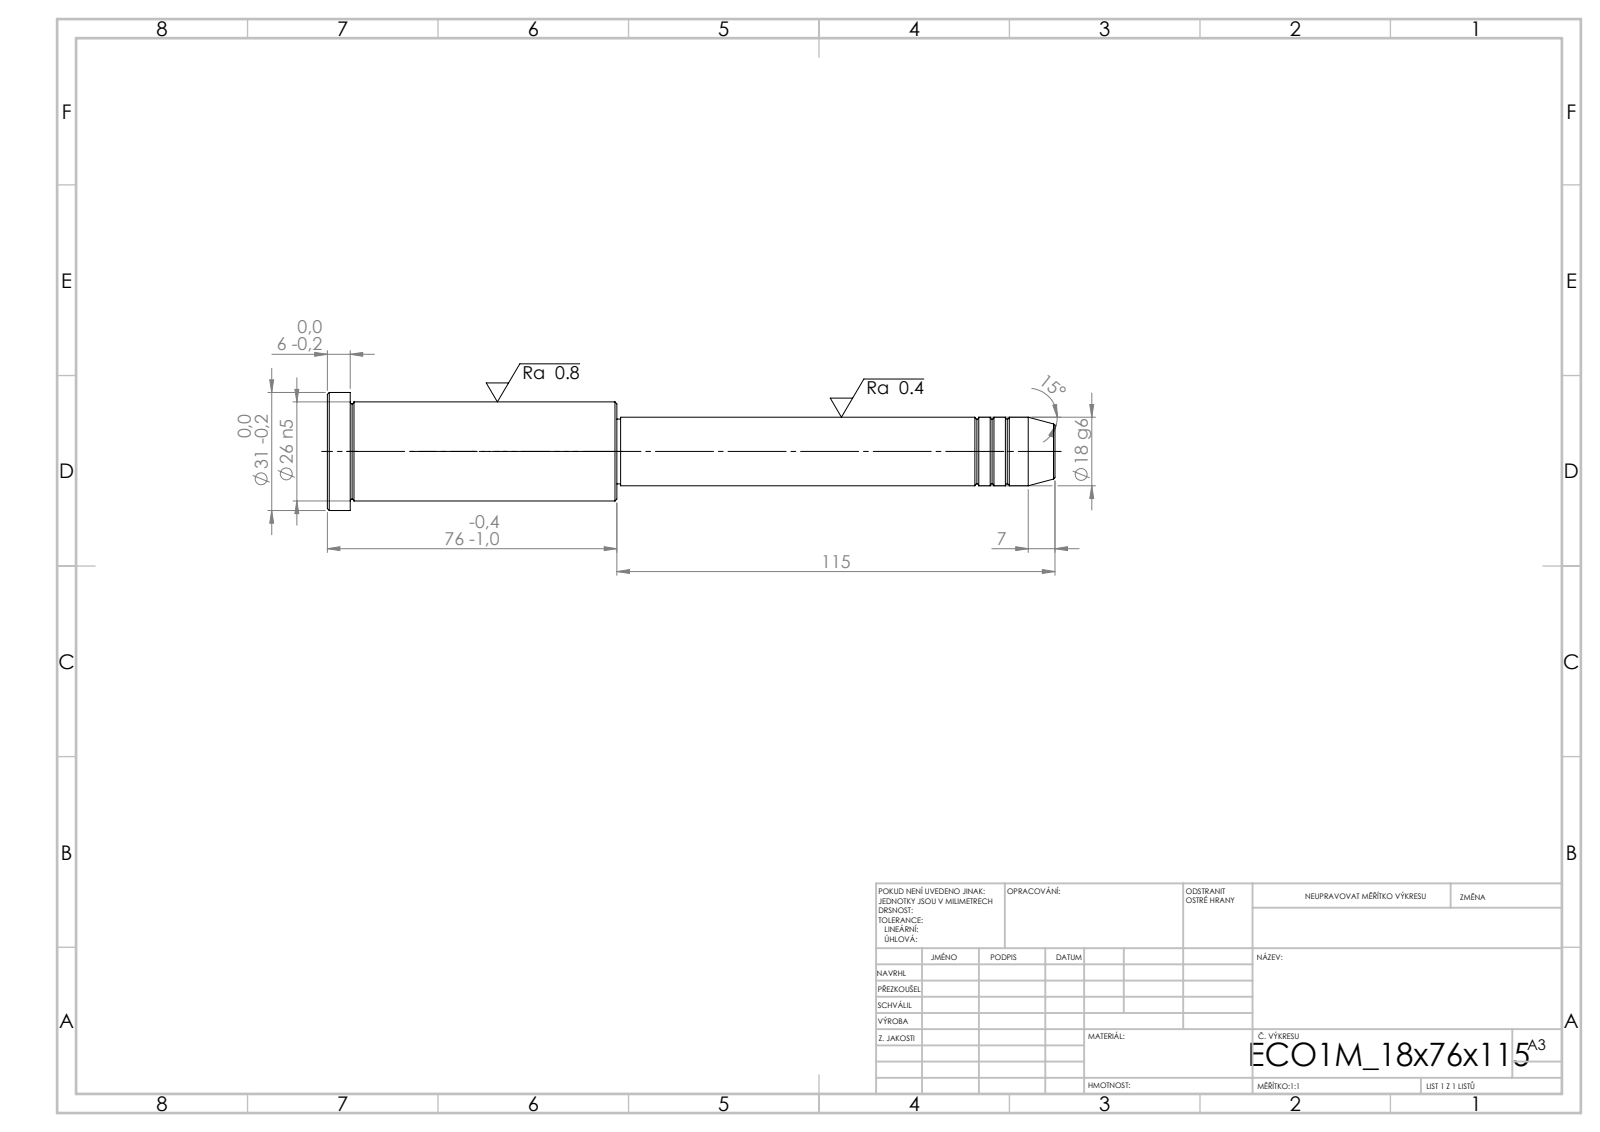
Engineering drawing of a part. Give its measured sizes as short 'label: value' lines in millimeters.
written by: SolidWorks 2019 (CONFIG_CONTROL_DESIGN)
unit: mm
bodies: 1 solid, 43 faces (5 planar, 14 cylindrical, 24 other)
size: 191 × 31 × 31
volume: 70 465 mm³; area: 14 315 mm²
bosses: 1× ⌀31, 1× ⌀26, 1× ⌀18, 1× ⌀17
face distances: 76, 70, 6, 115, 185, 191, 114, 1, 71, 77
